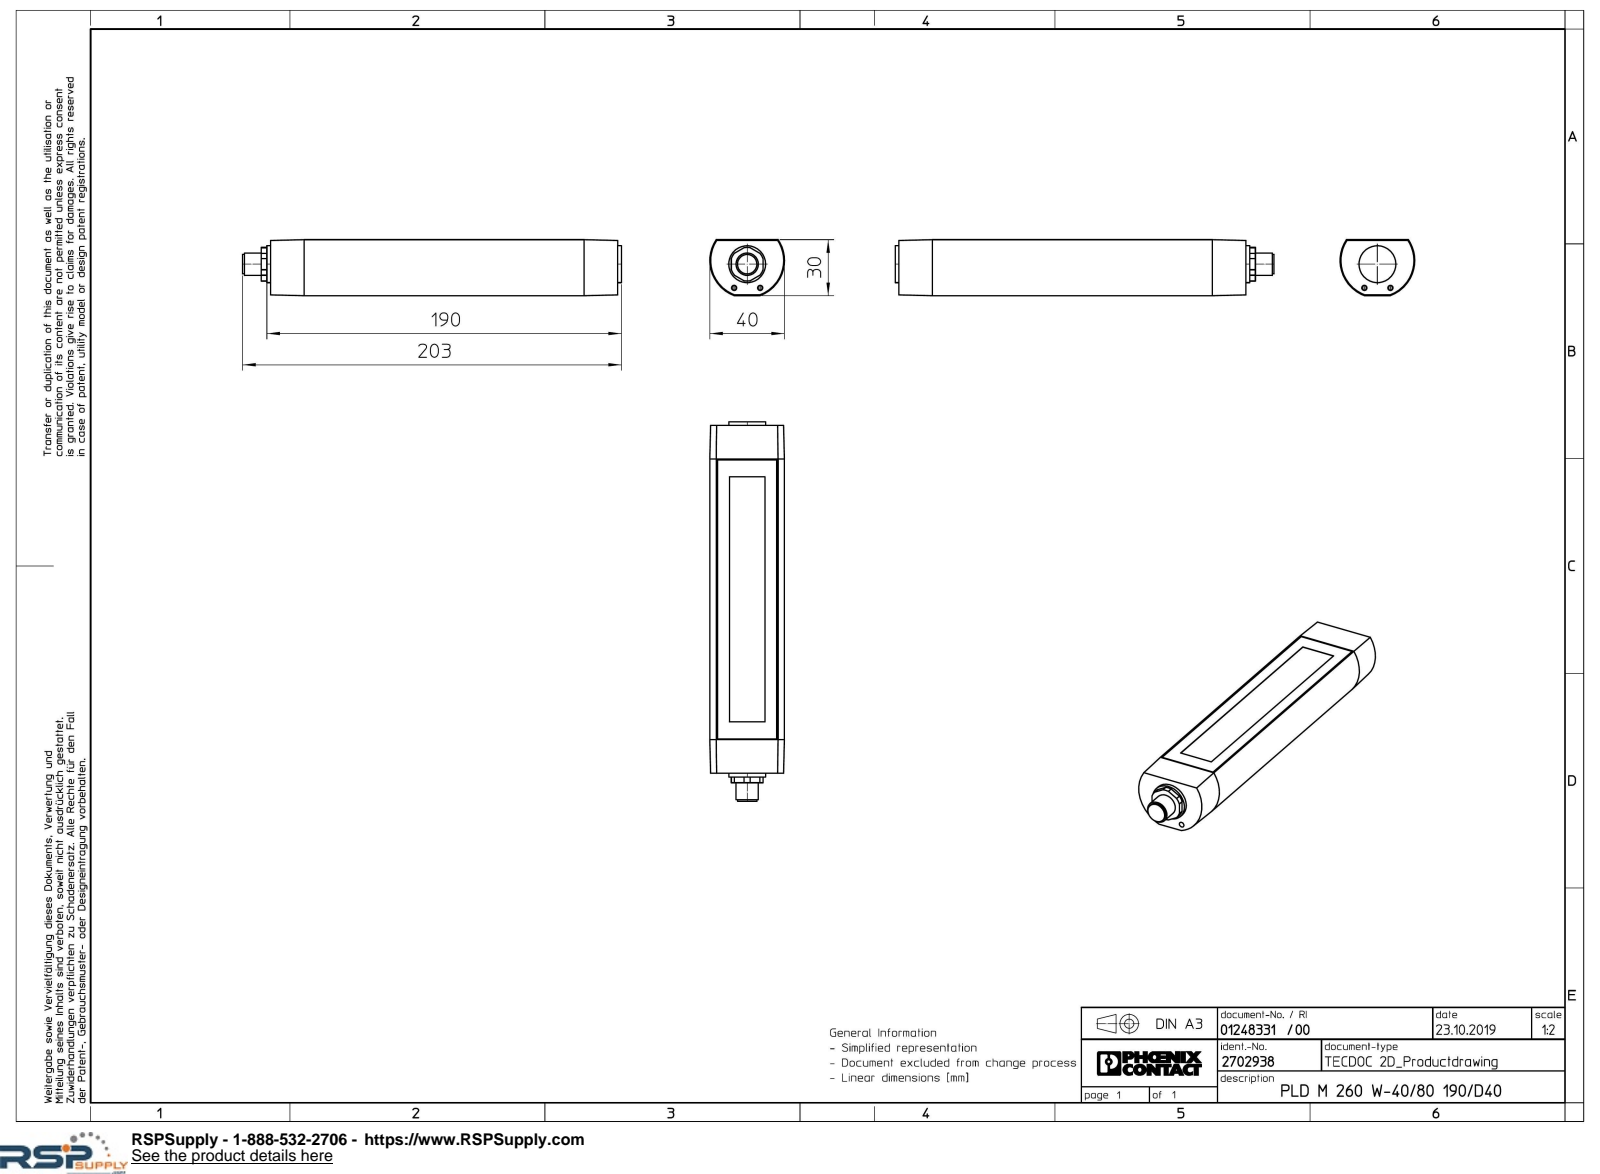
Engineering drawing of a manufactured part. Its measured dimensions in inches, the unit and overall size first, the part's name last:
Units: inches
Overall size (bounding box): 7.992 × 1.575 × 1.179
Round bosses / shafts (diameter × count): ⌀0.778 ×1, ⌀0.472 ×1, ⌀0.409 ×1
Partial cylindrical surfaces — rounded edges, fillets, slot ends (radius × count): R0.354 ×1, R0.787 ×1
Main face-to-face distances: 1.171, 1.175, 7.323, 0.079, 7.402, 1.179, 1.321, 1.32, 0.197, 7.52
Volume: 11.87 in³ · Surface area: 39.32 in²
Bodies: 1 solid, 61 faces (33 planar, 16 cylindrical, 12 other)
Part name (STEP PRODUCT): PLD_M_260_W_40_80_190_D40-select
STEP written by: Creo Elements/Direct Modeling 20.1A 29-Sep-2018 (C) Parametric Technology GmbH (AUTOMOTIVE_DESIGN)
